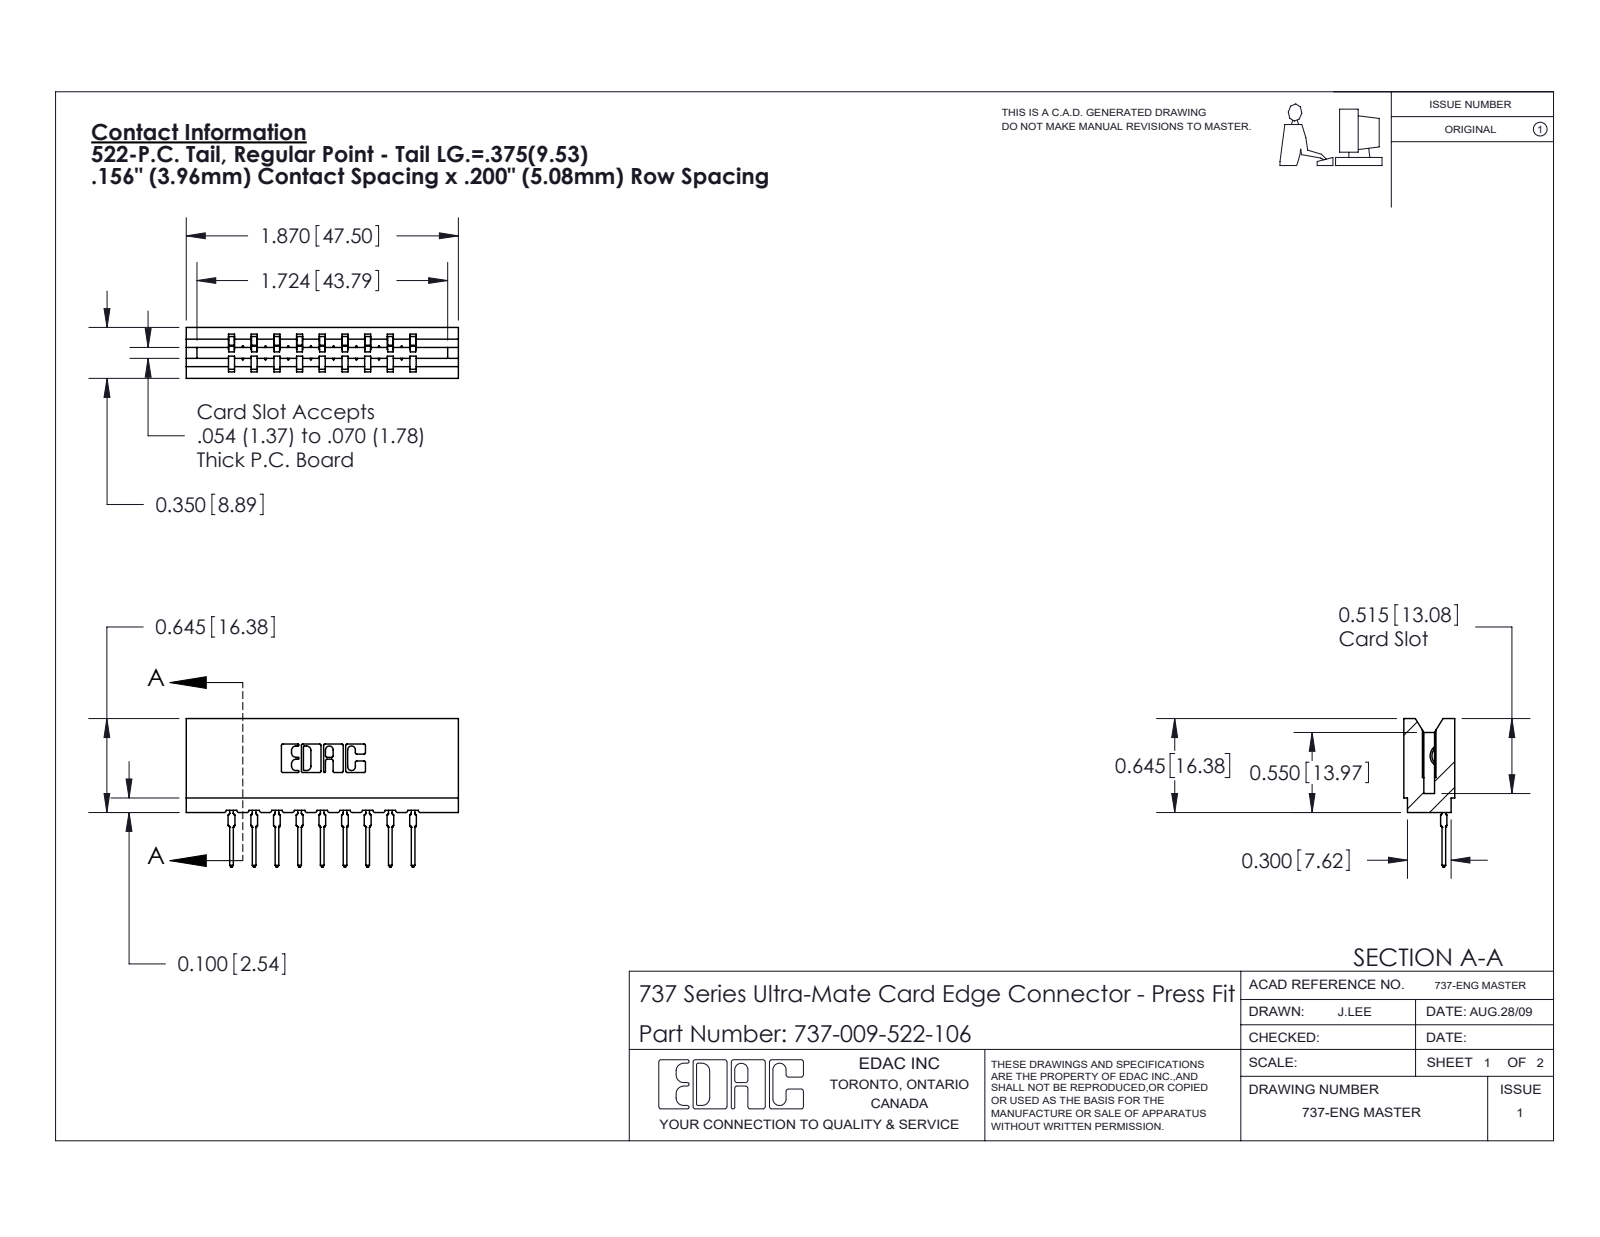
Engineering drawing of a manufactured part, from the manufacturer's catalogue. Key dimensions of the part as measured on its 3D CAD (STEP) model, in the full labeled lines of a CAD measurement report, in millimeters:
Part name (STEP PRODUCT): 737-009-522-106; 737 Part_Insulator Option - 06; 745-292-001_522
STEP written by: SolidWorks 2020 (CONFIG_CONTROL_DESIGN)
Units: millimetres
Bodies: 10 solids, 1112 faces (667 planar, 211 cylindrical, 234 other)
Overall size (bounding box): 47.5 × 25.9 × 8.9
Volume: 4 800 mm³ · Surface area: 5 876 mm²
Partial cylindrical surfaces — rounded edges, fillets, slot ends (radius × count): R0.3 ×22, R0.4 ×18, R0.5 ×18, R0.2 ×6, R0.8 ×6, R0.1 ×4, R0.3 ×4, R0.7 ×3
Main face-to-face distances: 4, 3.5, 5.4, 15.8, 8.9, 7.9, 11.9, 9, 5, 19.8
